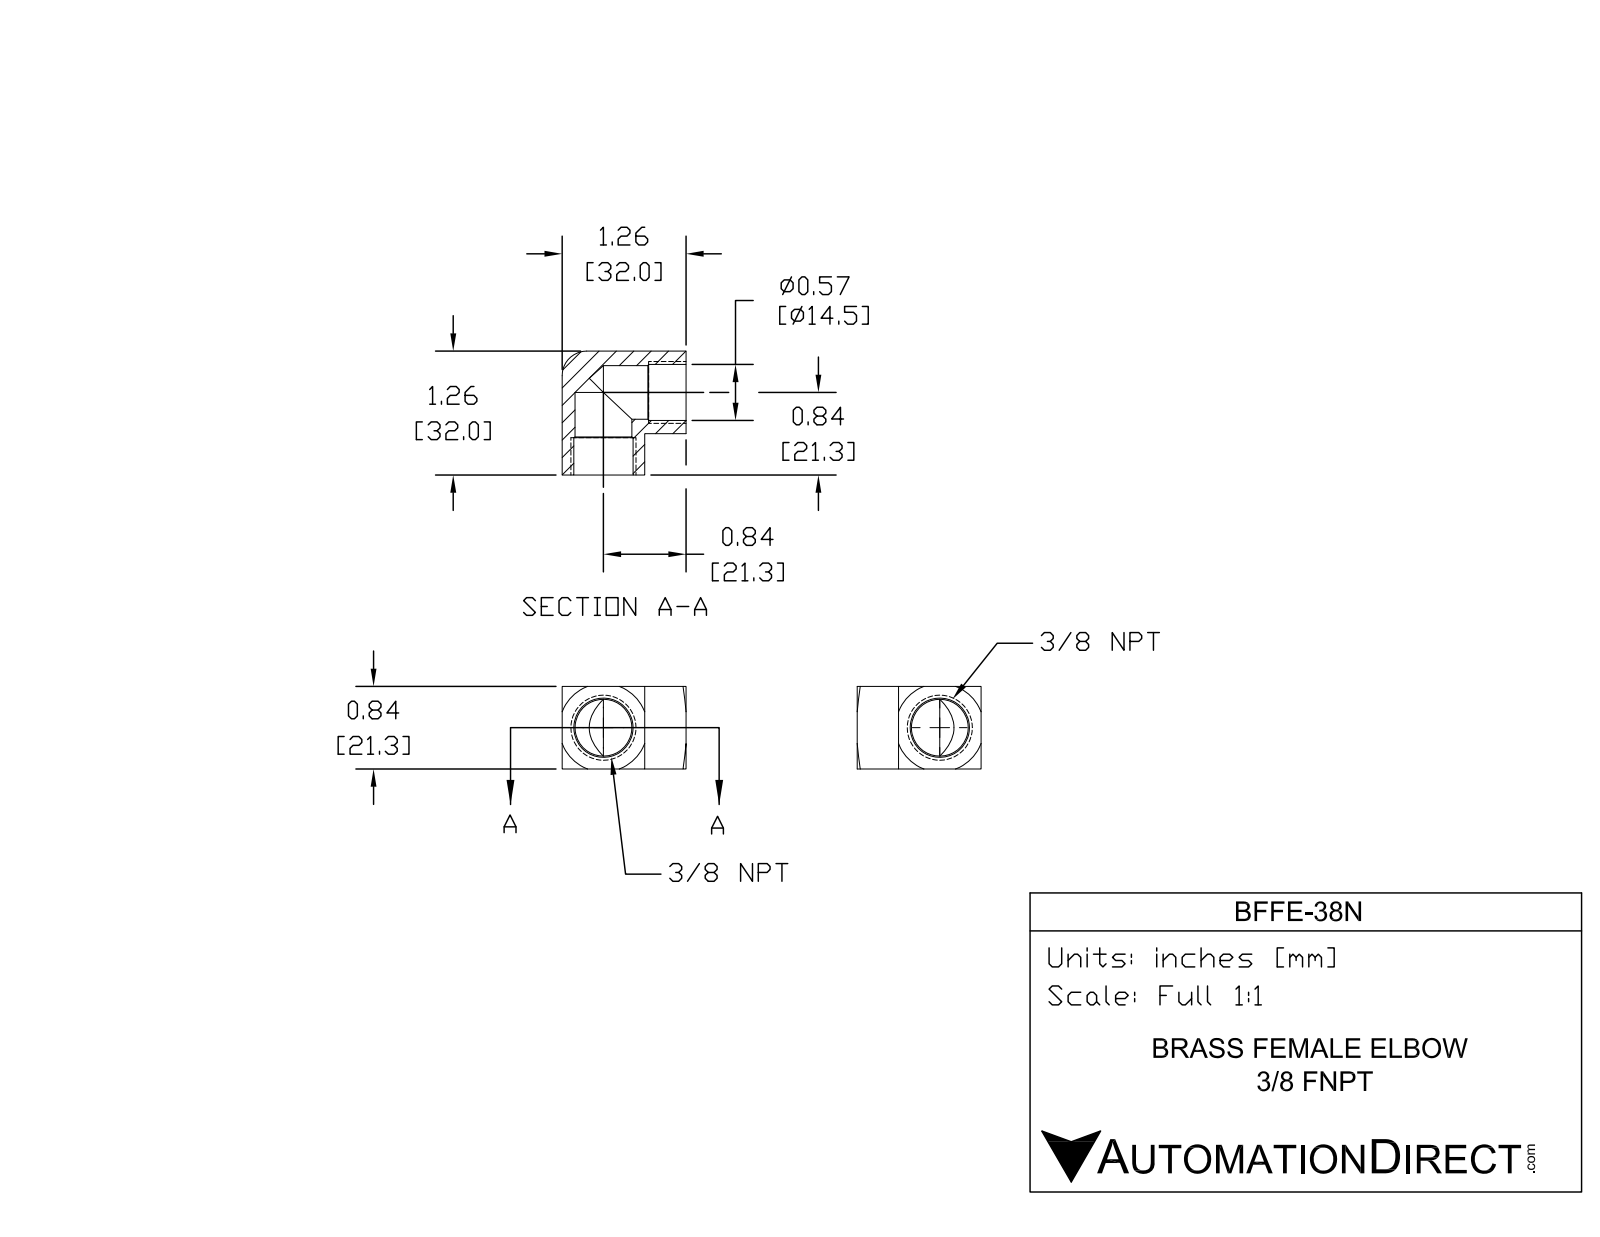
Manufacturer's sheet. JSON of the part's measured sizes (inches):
{"part_name": "BFFE-38N", "step_written_by": "SolidWorks 2015 (CONFIG_CONTROL_DESIGN)", "units": "inches", "bodies": {"solids": 1, "faces": 32, "planar": 8, "cylindrical": 9, "other": 15}, "overall_size": [1.26, 1.26, 0.84], "volume_in3": 0.731, "surface_area_in2": 9.332, "round_holes": [[0.578, 2], [0.603, 2]], "partial_cylinders_radius": [[0.25, 1]], "face_to_face_distances": [0.84, 1.26, 0.42]}
